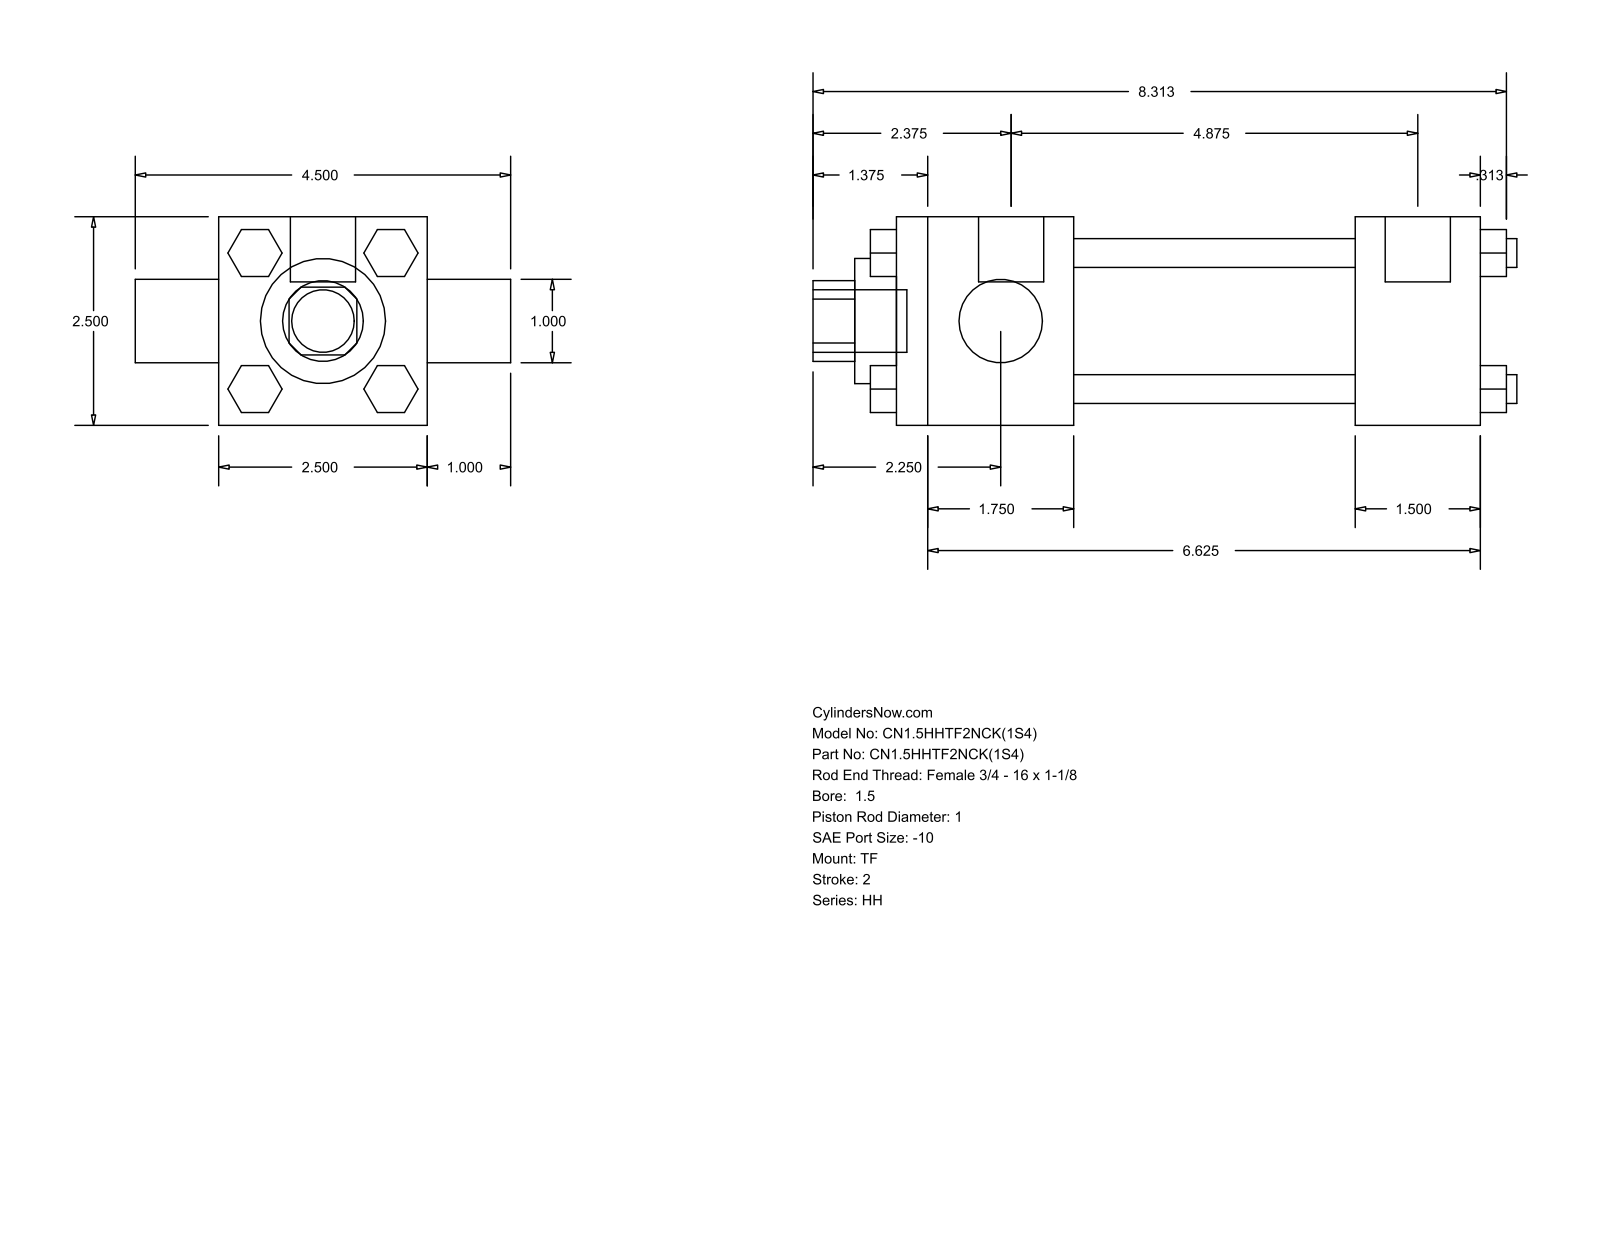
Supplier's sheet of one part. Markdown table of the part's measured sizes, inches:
| quantity | value |
| --- | --- |
| part name | HH_TF__0150_1 |
| STEP written by | GSSL Pune (CONFIG_CONTROL_DESIGN) |
| units | inches |
| bodies | 0 solids, 120 faces (92 planar, 28 cylindrical, 0 other) |
| overall size | 8.437 × 4.5 × 2.5 |
| round holes (diameter × count) | 1 × 2, 1.5 × 1, 1.75 × 1 |
| round bosses / shafts (diameter × count) | 0.345 × 4, 0.219 × 3, 0.781 × 2, 0.75 × 1 |
| partial cylindrical surfaces (radius × count) | 0.484 × 1 |
| main face-to-face distances | 2.5, 4.875, 3.375, 1.5, 2.125, 5.5, 7, 7.313, 1, 0.815 |
